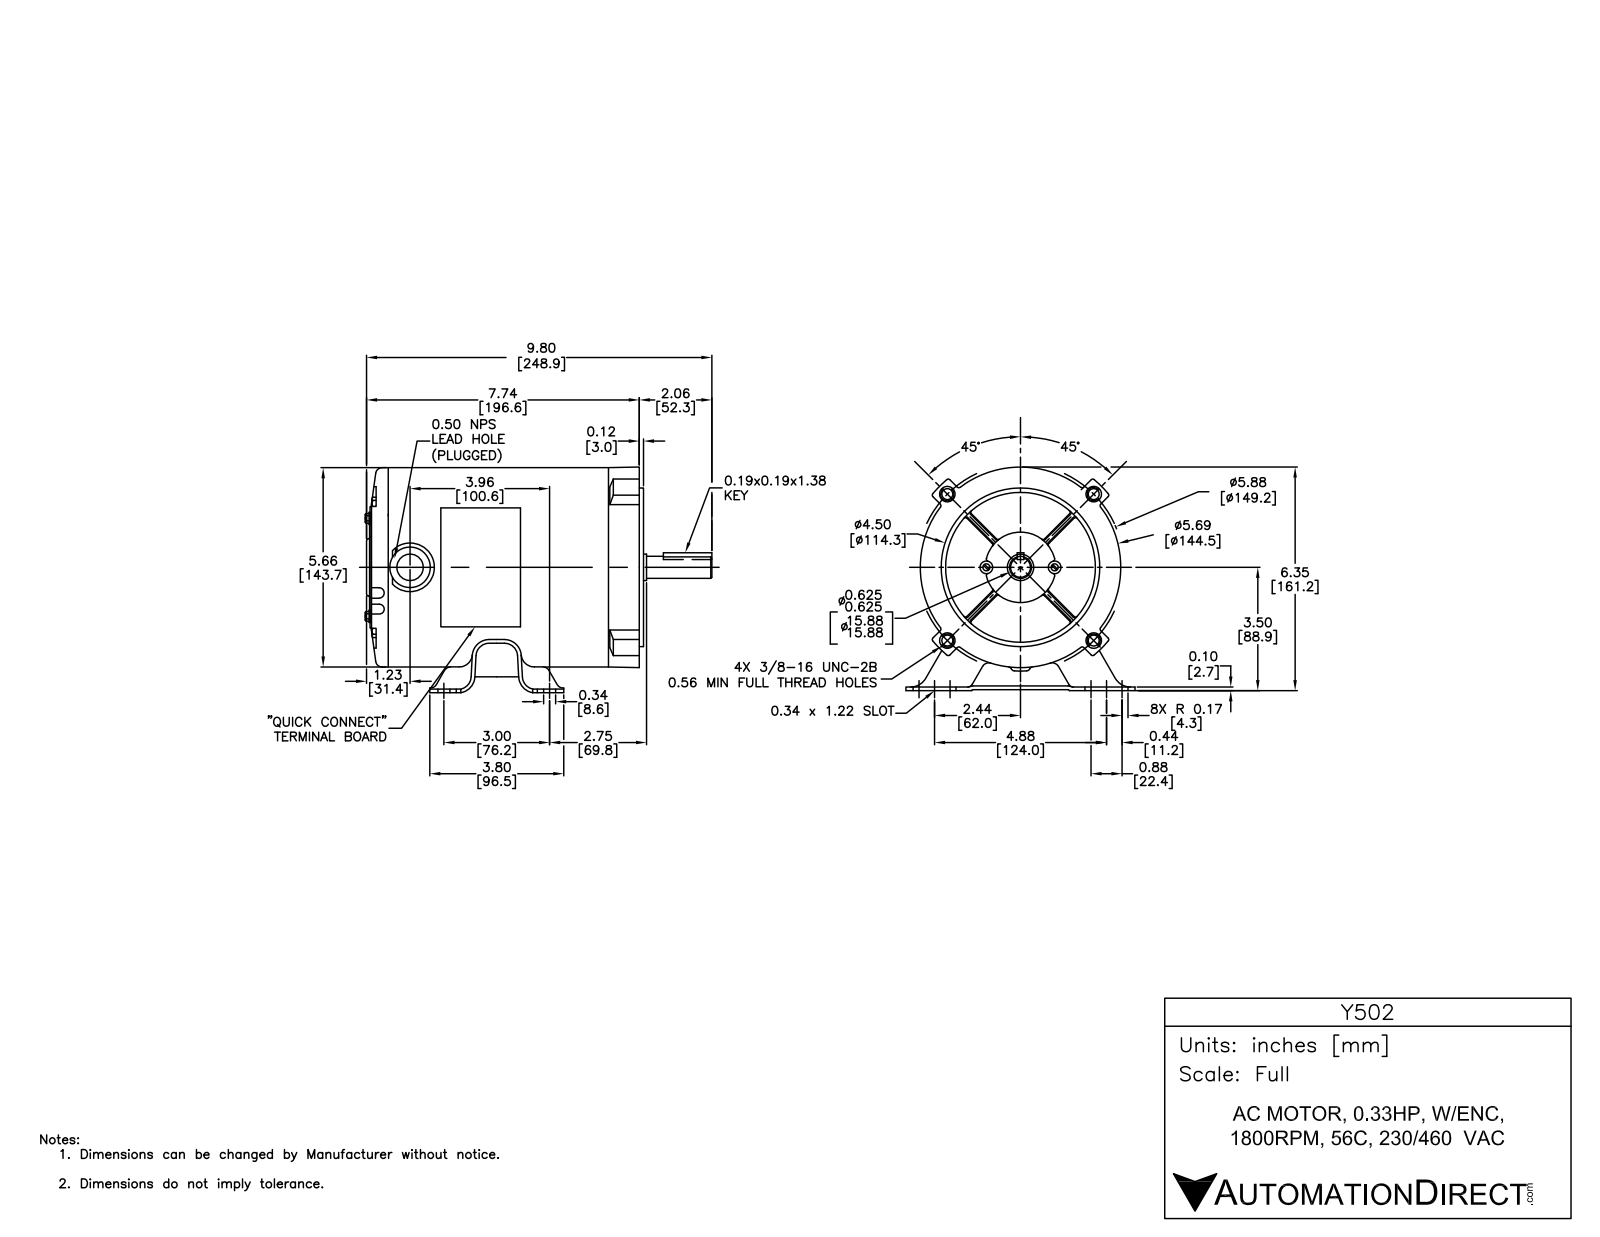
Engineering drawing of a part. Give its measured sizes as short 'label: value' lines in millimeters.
name: SS403144-625_Rev03 r1
written by: SolidWorks 2017 (AUTOMOTIVE_DESIGN)
unit: mm
bodies: 31 solids, 2886 faces (1021 planar, 684 cylindrical, 1181 other)
size: 251.3 × 165.1 × 159.9
volume: 434 300 mm³; area: 358 700 mm²
holes: 11× ⌀3.9, 4× ⌀3.4, 4× ⌀3.5, 4× ⌀5.6, 4× ⌀9.7, 2× ⌀3.8, 2× ⌀5.1, 2× ⌀5.5, 2× ⌀6, 2× ⌀7.1, 1× ⌀6.4, 1× ⌀11.6
bosses: 8× ⌀8.5, 4× ⌀4.2, 4× ⌀4.1, 4× ⌀3.6, 2× ⌀10.1, 2× ⌀4.8, 1× ⌀142.7, 1× ⌀139.6
rounds: 47× R1.5, 41× R1.3, 31× R0.8, 14× R2.3, 14× R4.3, 13× R0.5, 12× R4.1, 12× R9.7
face distances: 2.6, 1.5, 0.4, 192.9, 194.4, 2.5, 1, 2.3, 3.6, 189.4
hole spacings: 92, 92, 92, 99, 99, 99, 130.1, 130.2
